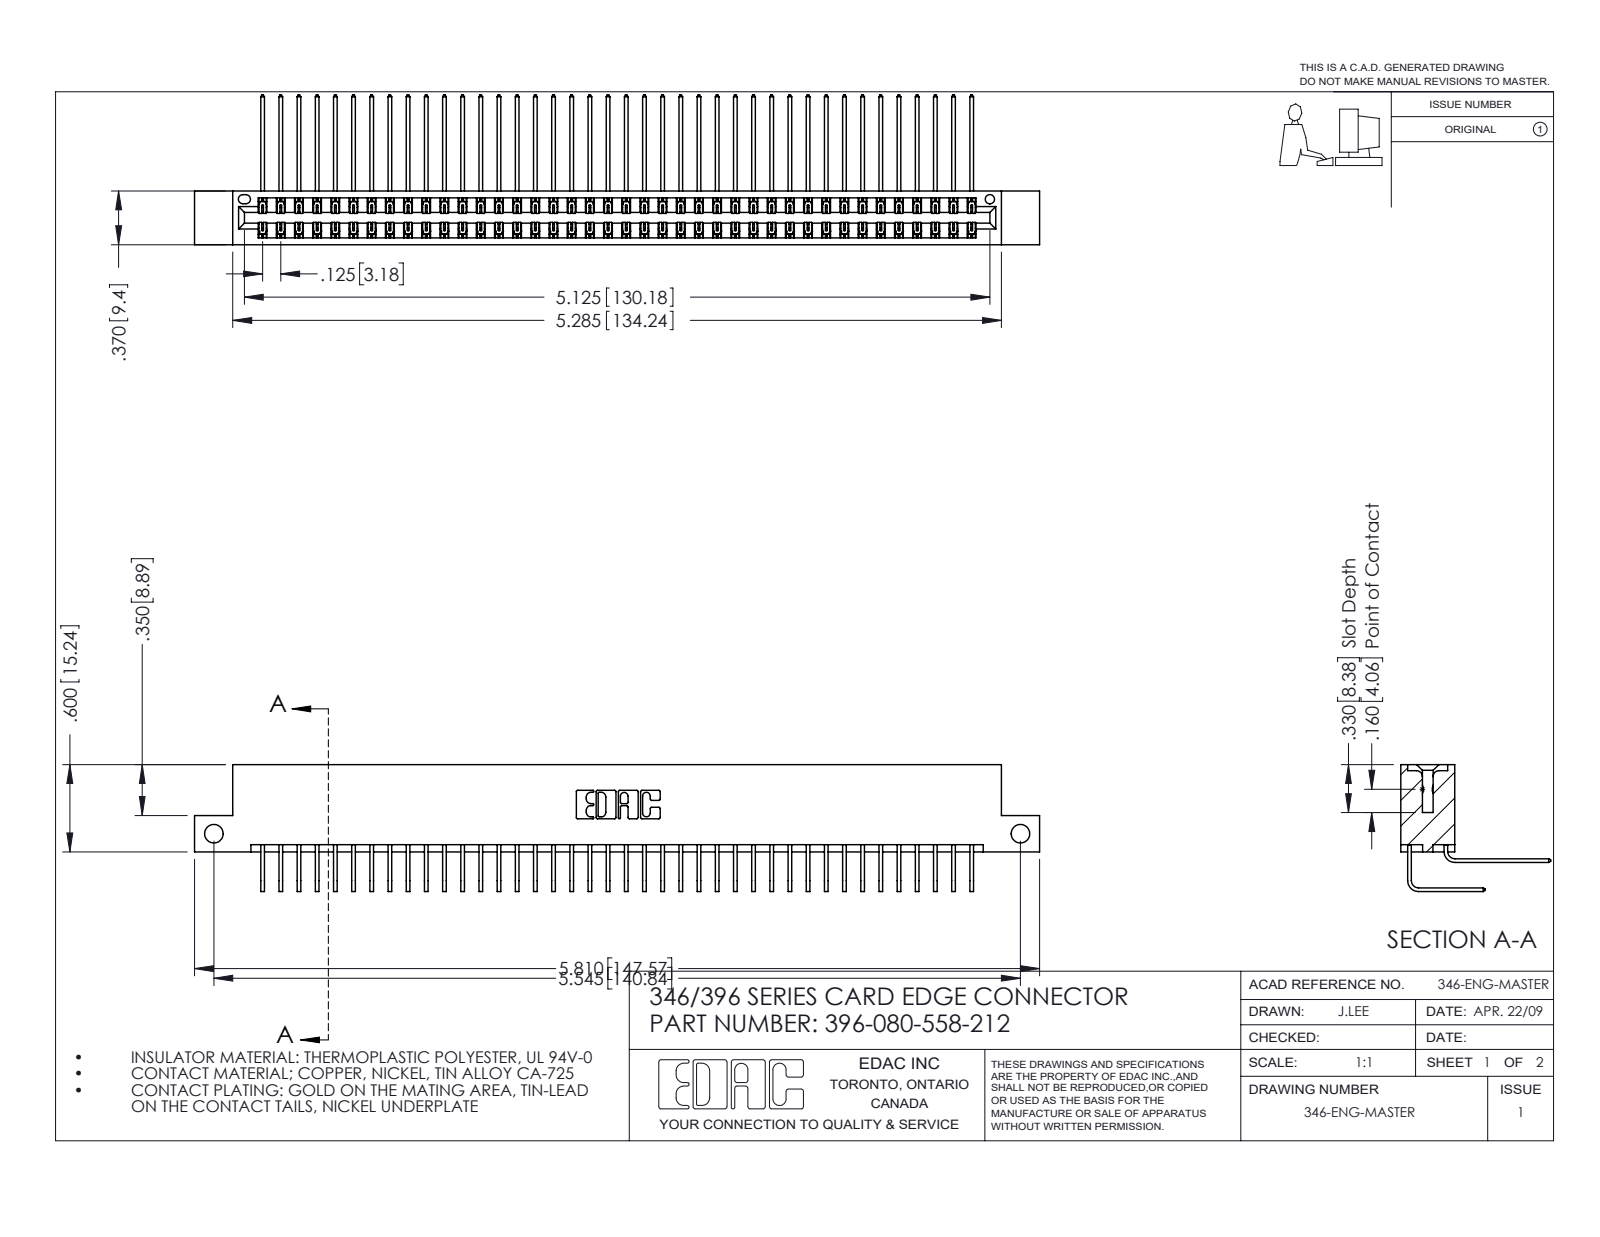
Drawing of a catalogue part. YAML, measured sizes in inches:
part_name: "346 Part_Flush Mounting Lugs - Side Mount; 345-292-001_558 Tail - 2; 345-292-001_558 559 Tail - 1; 396-080-558-212"
step_written_by: "SolidWorks 2016 (CONFIG_CONTROL_DESIGN)"
units: inches
bodies: {solids: 81, faces: 4442, planar: 3036, cylindrical: 1406, other: 0}
overall_size: [5.81, 1.03, 0.873]
volume: 0.9
surface_area: 34.59
round_holes:
  - {diameter: 0.128, count: 2}
  - {diameter: 0.064, count: 1}
partial_cylinders:
  - {radius: 0.006, count: 120}
  - {radius: 0.01, count: 22}
  - {radius: 0.007, count: 6}
  - {radius: 0.031, count: 6}
  - {radius: 0.026, count: 3}
  - {radius: 0.014, count: 2}
  - {radius: 0.022, count: 2}
  - {radius: 0.024, count: 2}
face_to_face_distances: [0.048, 0.322, 0.025, 0.25, 0.37, 0.072, 0.298, 0.275, 0.148, 0.222]
hole_center_spacings: [5.545]
